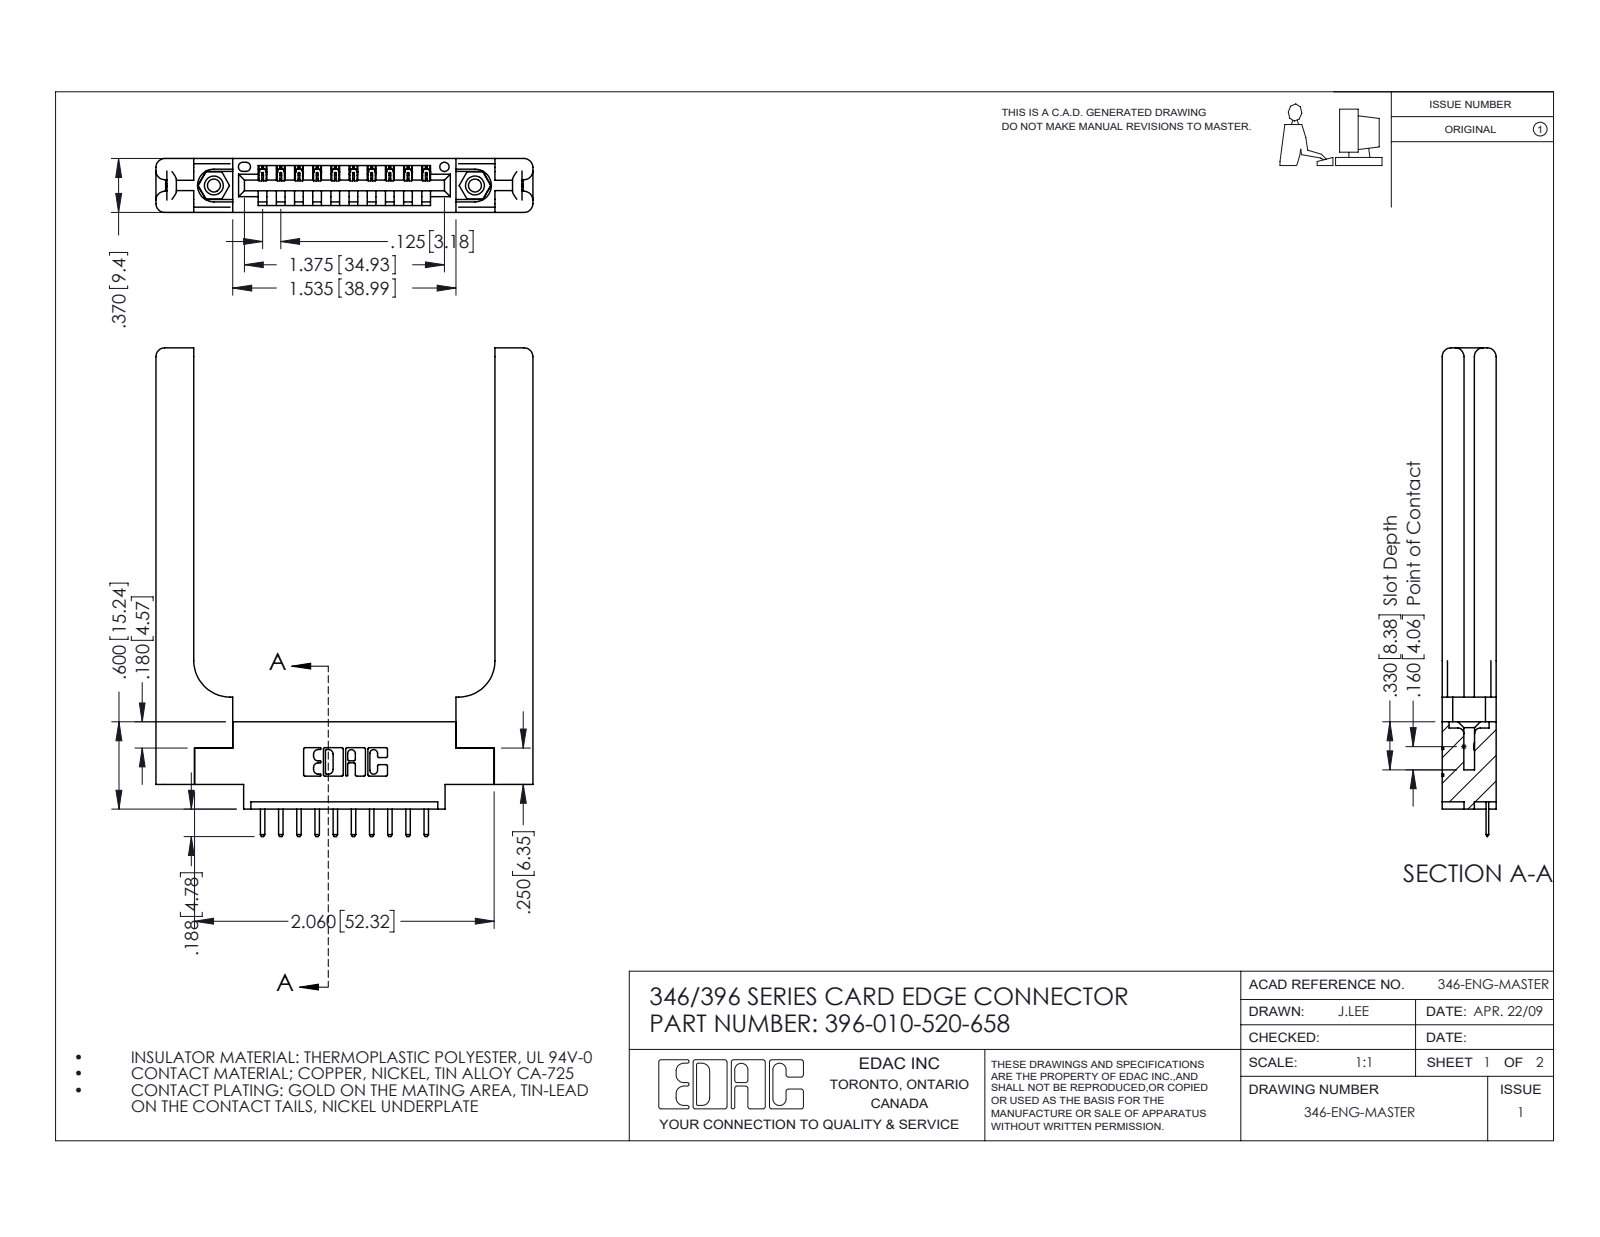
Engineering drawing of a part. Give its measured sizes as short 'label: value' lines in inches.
name: 345-250-001_345-250-001-102; 396-010-520-658; 346-220-058_345-220-058; 346 Part_0.170 Offset - 0.156 Dia-TH (+1 more)
written by: SolidWorks 2016 (CONFIG_CONTROL_DESIGN)
unit: in
bodies: 15 solids, 1002 faces (648 planar, 294 cylindrical, 60 other)
size: 3.358 × 2.591 × 0.37
volume: 0.819 in³; area: 19 in²
holes: 2× ⌀0.089, 2× ⌀0.125, 2× ⌀0.156, 1× ⌀0.064
bosses: 2× ⌀0.155
rounds: 22× R0.01, 22× R0.01, 20× R0.006, 16× R0.06, 6× R0.007, 6× R0.031, 3× R0.026, 2× R0.03
face distances: 0.37, 0.15, 0.22, 0.072, 0.148, 0.25, 0.102, 0.048, 0.322, 0.173
hole spacings: 0.246, 1.59, 1.795
